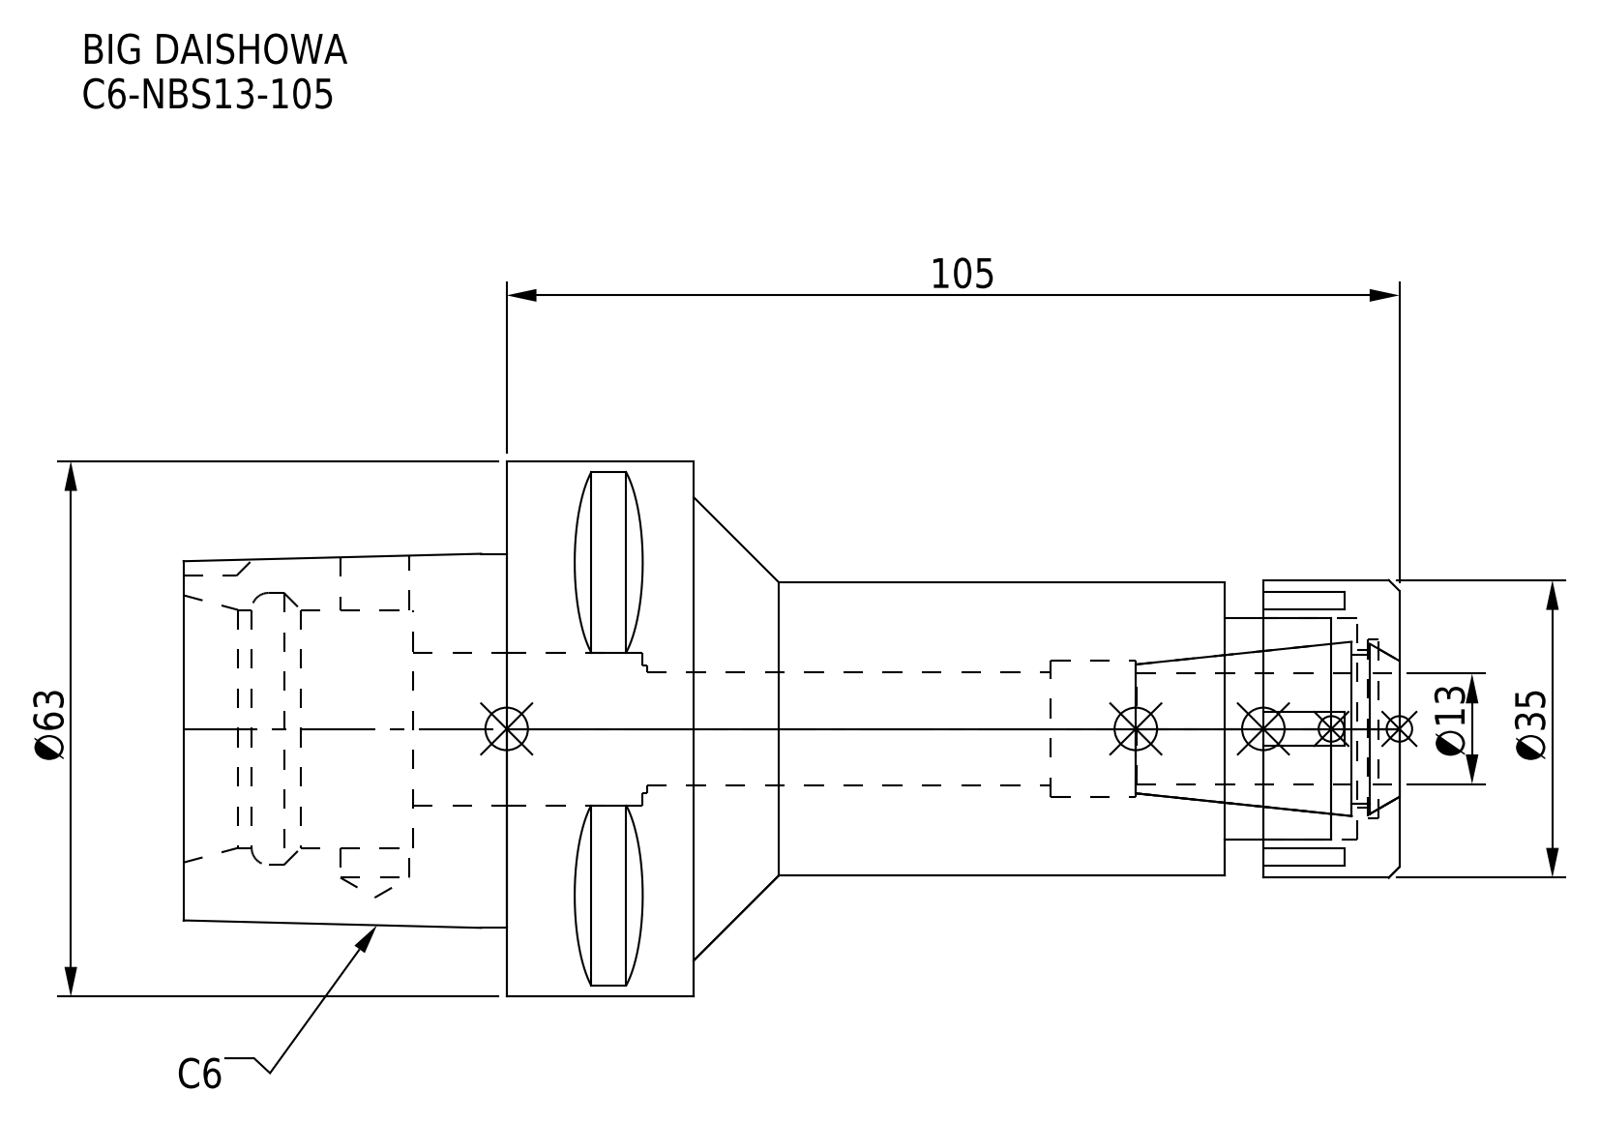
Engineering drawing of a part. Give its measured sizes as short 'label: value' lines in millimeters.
name: C6-NBS13-105.stp; NBN13_1.stp; C6-NBS13-105-130_ASM.stp; C6-NBS13-105 (+3 more)
written by: SolidWorks 2019 (CONFIG_CONTROL_DESIGN)
unit: mm
bodies: 2 solids, 112 faces (61 planar, 33 cylindrical, 18 other)
size: 143 × 63 × 63
volume: 161 341 mm³; area: 35 607 mm²
holes: 1× ⌀8.1, 1× ⌀13.3, 1× ⌀15, 1× ⌀16, 1× ⌀18, 1× ⌀18.5, 1× ⌀21, 1× ⌀26, 1× ⌀28, 1× ⌀32
bosses: 1× ⌀63, 1× ⌀35, 1× ⌀34.5
rounds: 1× R5
face distances: 22, 83, 105, 11, 100, 143, 60, 38, 20.5, 16
